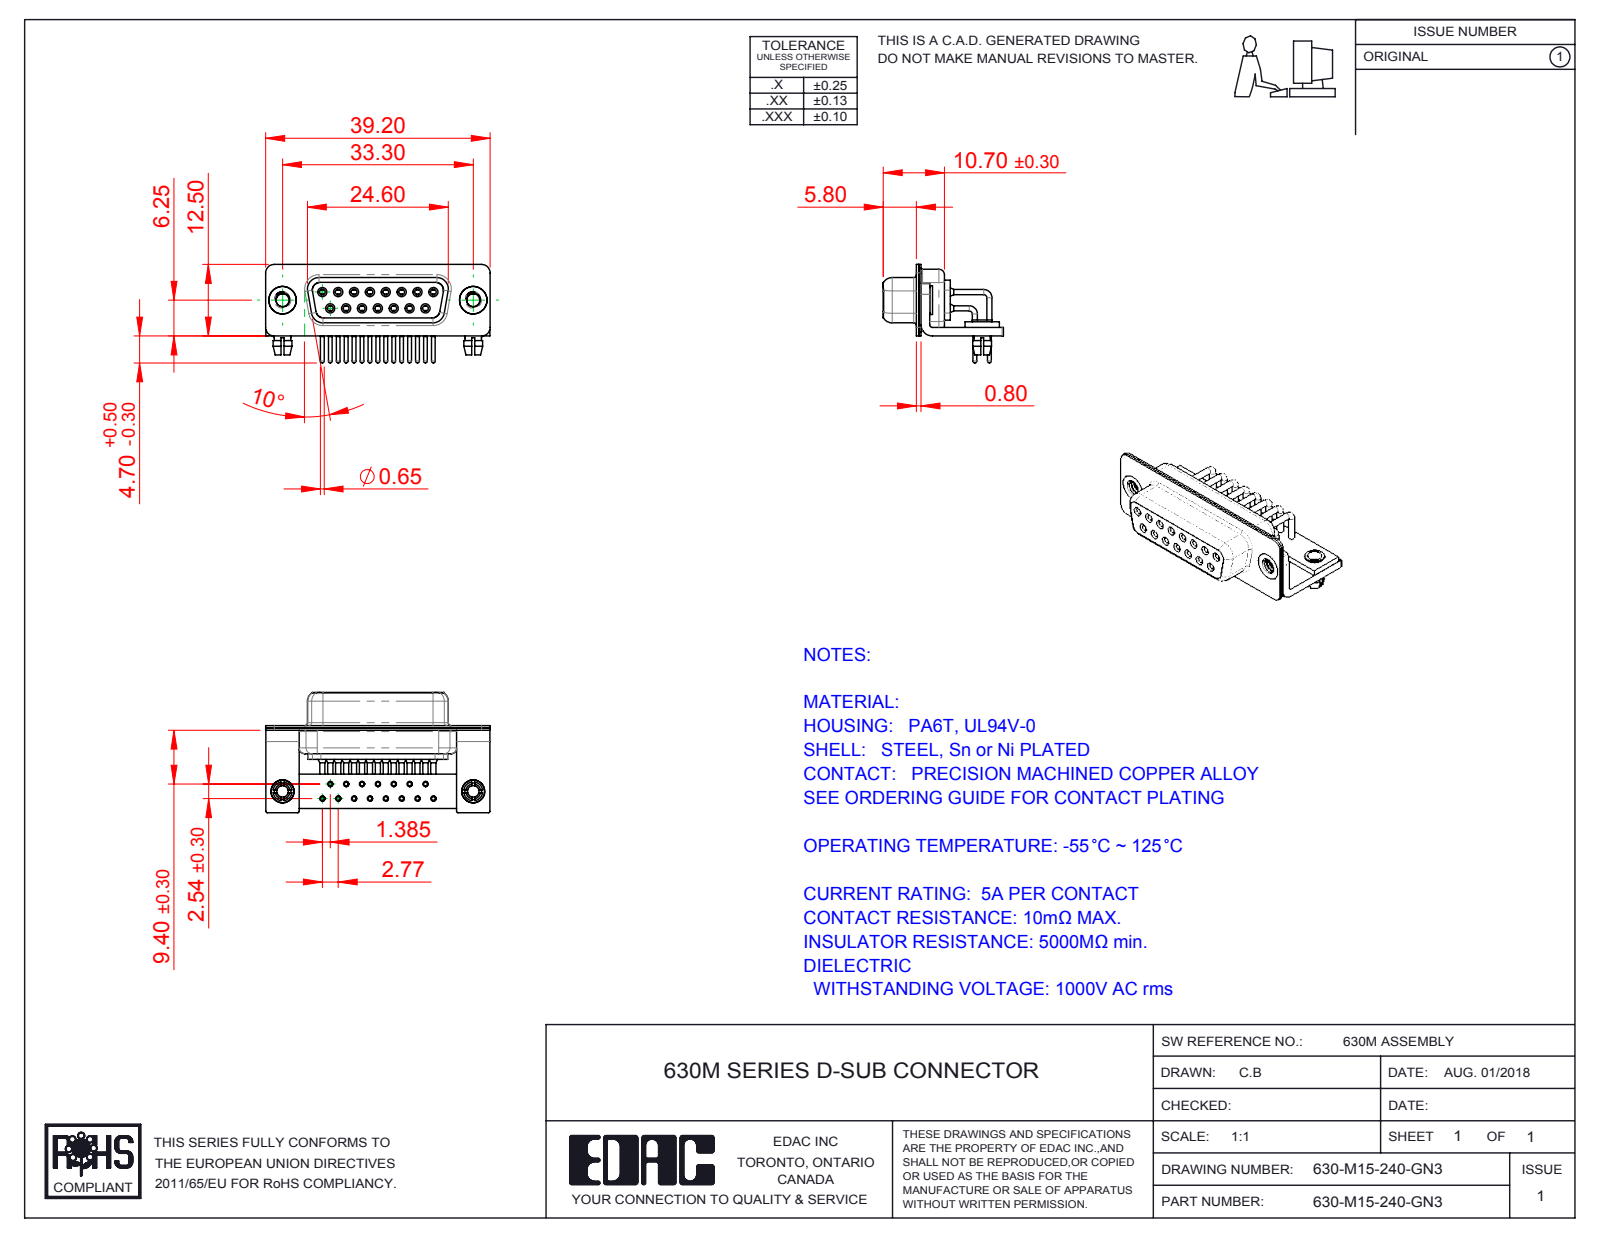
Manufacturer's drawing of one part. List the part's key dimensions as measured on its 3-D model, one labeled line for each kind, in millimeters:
Part name (STEP PRODUCT): 630M Contact Row 1; 630-M15-240-GN3; 630M Shell Front_15 Contacts; 630M Shell Rear_15 Contacts (+6 more)
STEP written by: SolidWorks 2016 (CONFIG_CONTROL_DESIGN)
Units: millimetres
Bodies: 25 solids, 1246 faces (366 planar, 566 cylindrical, 314 other)
Overall size (bounding box): 39.2 × 21 × 17.2
Volume: 3 090 mm³ · Surface area: 7 958 mm²
Round holes (diameter × count): ⌀2 ×17, ⌀0.9 ×15, ⌀1 ×15, ⌀1.1 ×15, ⌀1.7 ×15, ⌀1.8 ×15, ⌀2.26 ×2, ⌀2.5 ×2, ⌀3.2 ×2, ⌀4 ×2, ⌀4.8 ×2
Round bosses / shafts (diameter × count): ⌀0.9 ×27, ⌀1.6 ×15, ⌀1.5 ×15, ⌀0.65 ×15, ⌀5 ×2, ⌀4.9 ×2, ⌀4 ×2, ⌀3.4 ×2
Partial cylindrical surfaces — rounded edges, fillets, slot ends (radius × count): R0.25 ×16, R1.5 ×16, R2 ×13, R1.35 ×8, R1.6 ×8, R0.5 ×5, R0.6 ×4, R0.65 ×4
Main face-to-face distances: 0.4, 0.8, 2.3, 1.5, 9.35, 1.9, 1, 1.45, 8.95, 0.85
Hole centre spacings: 2.77, 5.54, 8.31, 3.16, 4.87, 11.08, 2.89, 7.37
